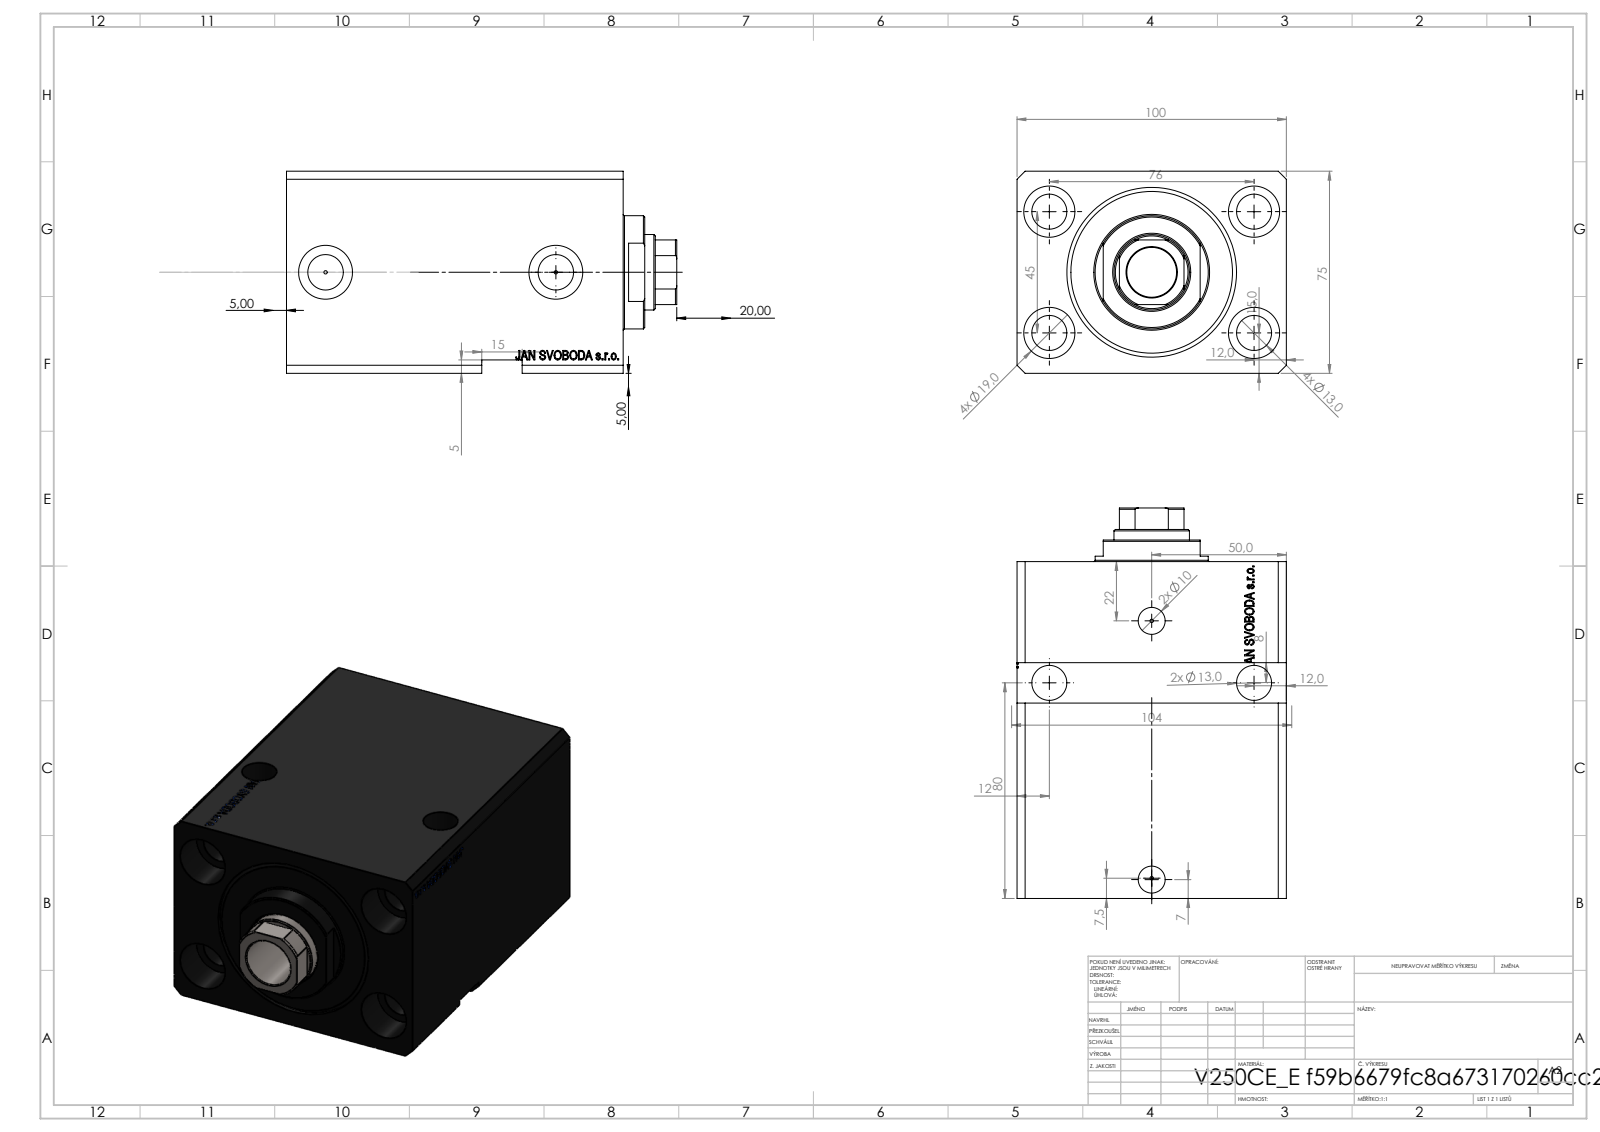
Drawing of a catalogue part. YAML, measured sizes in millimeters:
part_name: "V250CE_VC_E; V250CE_C_VCP; V250CE_E_Body"
step_written_by: "SolidWorks 2019 (CONFIG_CONTROL_DESIGN)"
units: millimeters
bodies: {solids: 3, faces: 938, planar: 459, cylindrical: 104, other: 375}
overall_size: [145, 100, 75]
volume: 754695
surface_area: 138585
round_holes:
  - {diameter: 13, count: 8}
  - {diameter: 1.25, count: 4}
  - {diameter: 19, count: 4}
  - {diameter: 10, count: 2}
  - {diameter: 13.16, count: 2}
  - {diameter: 20, count: 2}
  - {diameter: 18.5, count: 1}
  - {diameter: 28, count: 1}
  - {diameter: 50, count: 1}
  - {diameter: 63, count: 1}
round_bosses_or_shafts:
  - {diameter: 42, count: 1}
partial_cylinders:
  - {radius: 13.5, count: 1}
face_to_face_distances: [75, 100, 125, 11.9, 113.1, 20, 105, 93.1, 70, 13]
hole_center_spacings: [44.16, 76, 40, 44.42, 45, 49.98, 50.33, 73.57]
